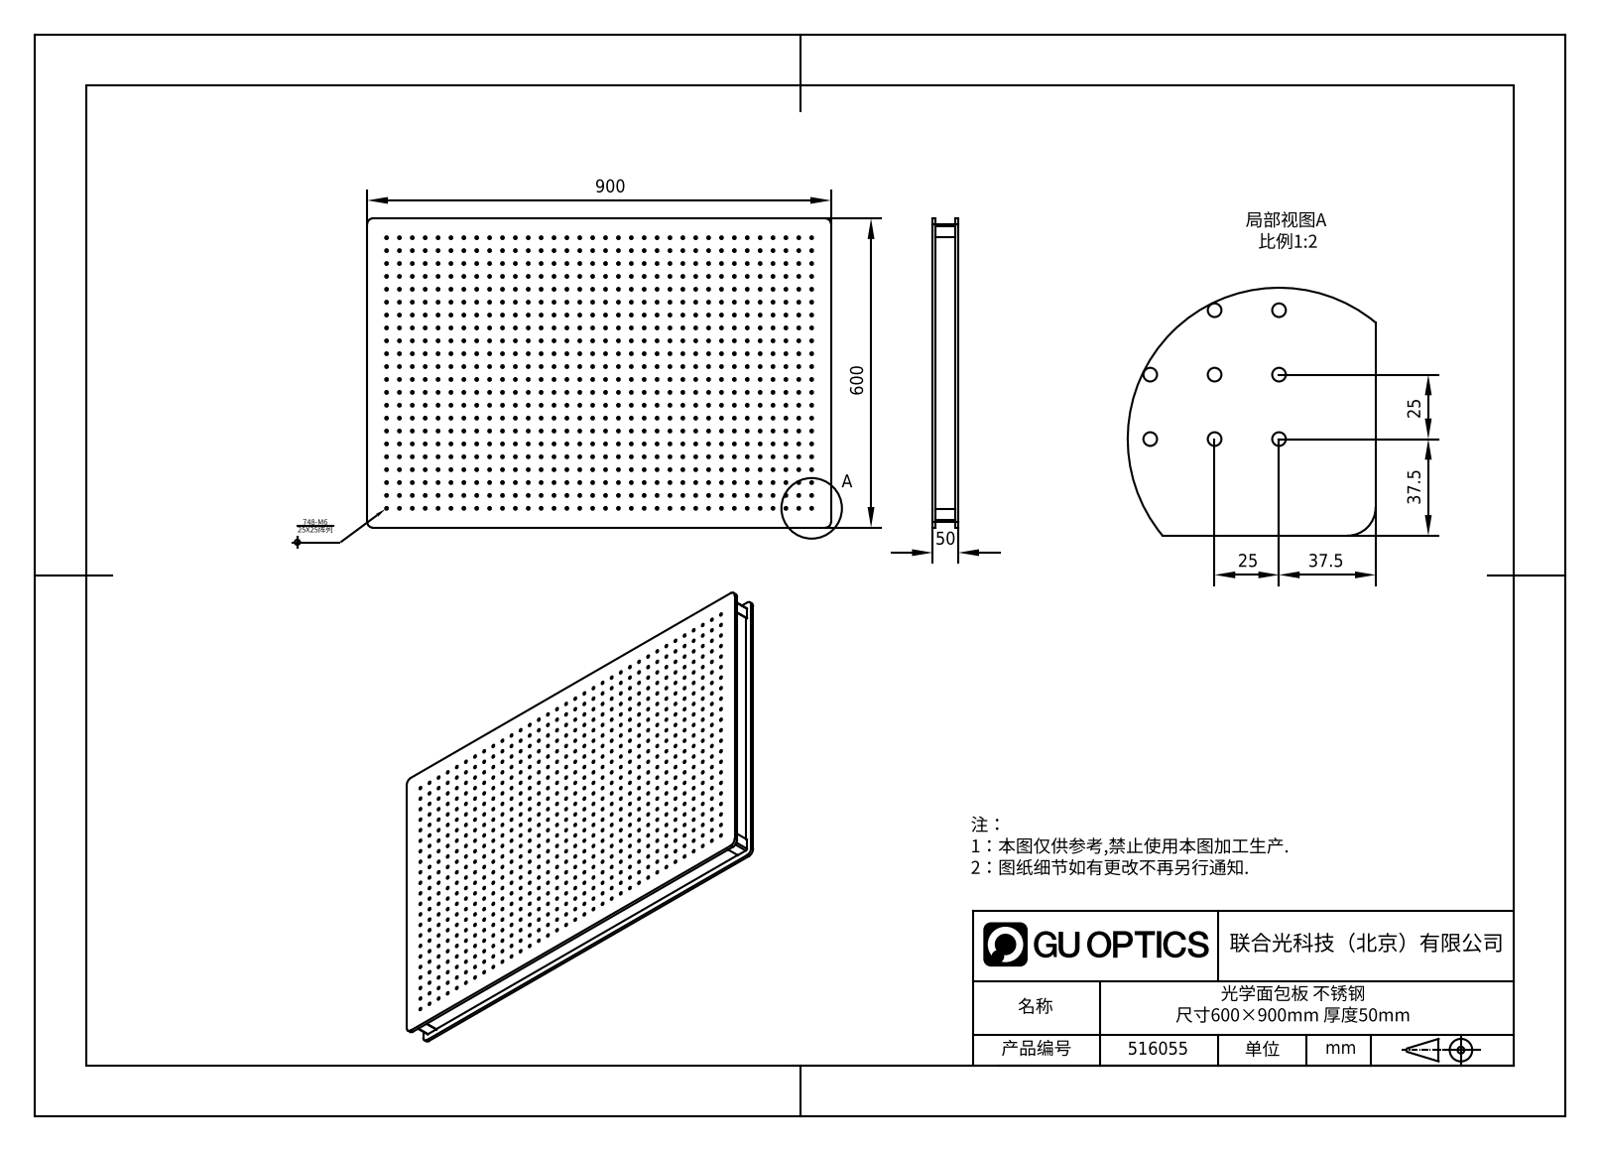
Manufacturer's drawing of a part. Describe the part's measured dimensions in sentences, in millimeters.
The part is named "516055". Its 3-D file was written by "SolidWorks 2020 (CONFIG_CONTROL_DESIGN)". It is 1 solid with 2304 faces: 792 planar, 1512 cylindrical and 0 other. Overall it measures 900 by 600 by 50 millimeters. Its volume is 25 410 000 cubic millimeters and its surface area 1 385 000 square millimeters. Round holes: 748 of diameter 5.3. Partial cylindrical surfaces (rounded edges, fillets, slot ends): 4 of radius 2, 4 of radius 3, 4 of radius 11. The main face-to-face distances are 50, 6, 44, 45, 39, 5, 574, 13, 874, 587. The hole center spacings are 25, 50, 75, 100, 125, 150, 175, 200.
